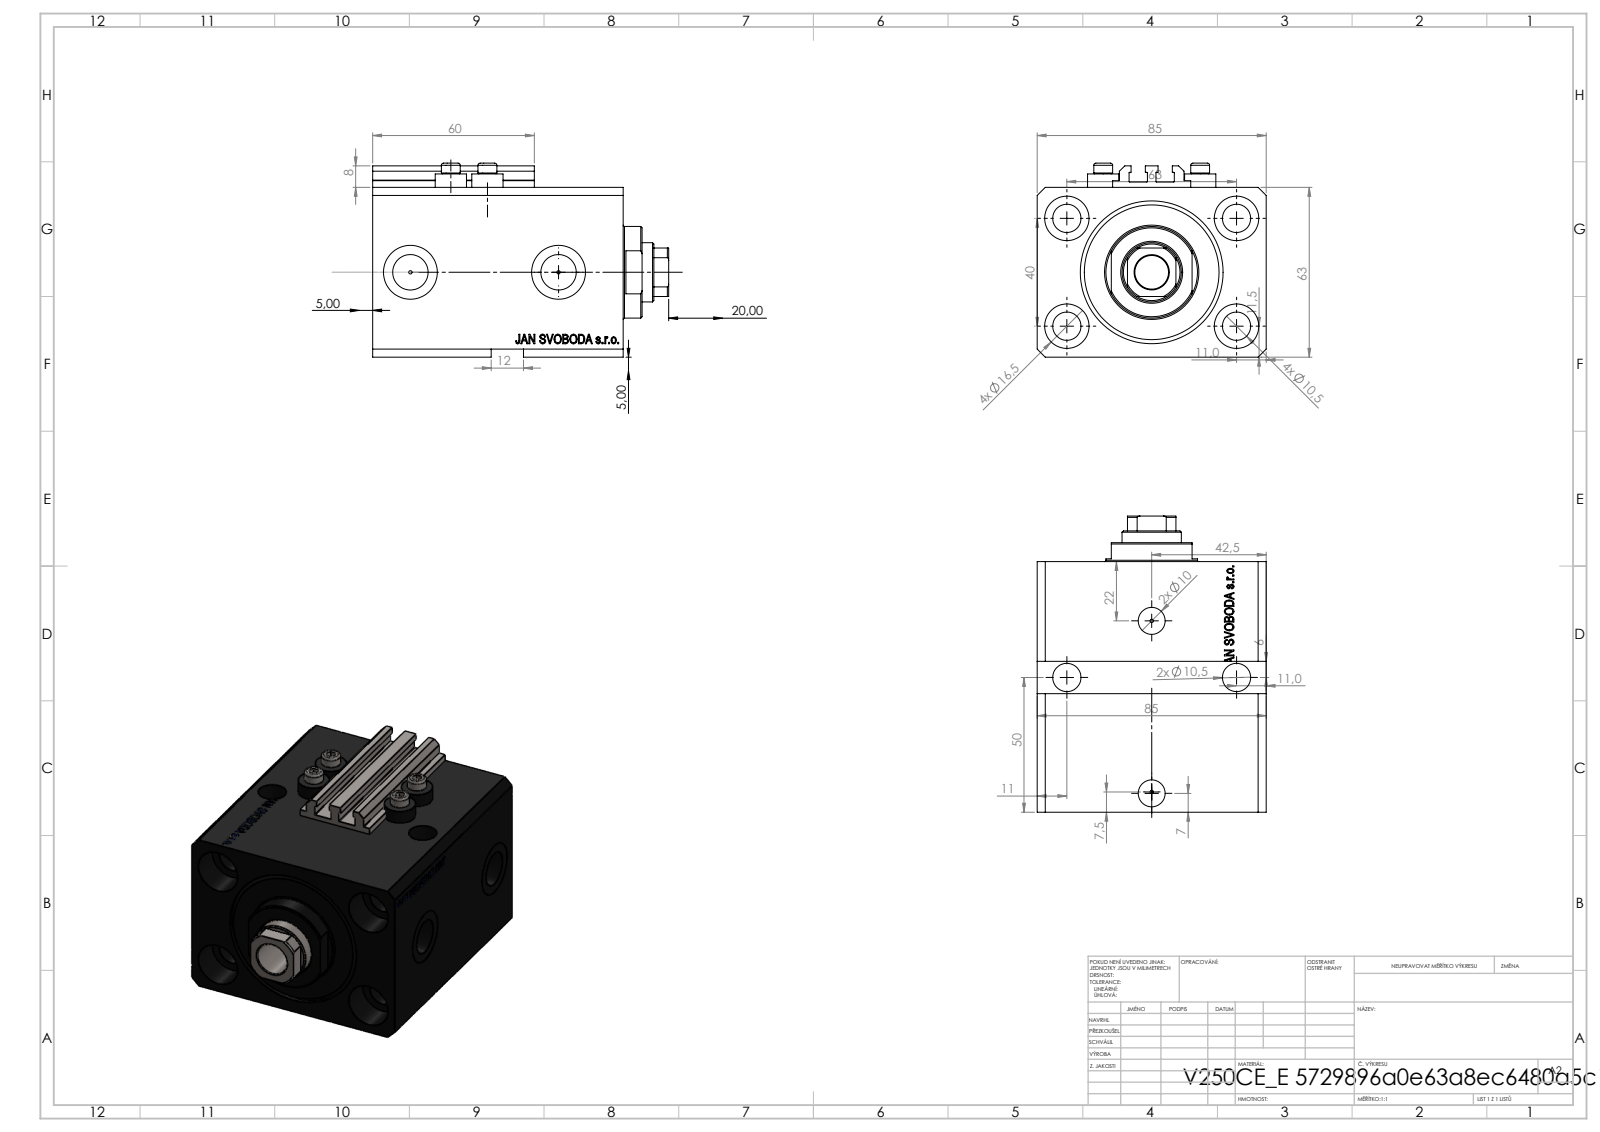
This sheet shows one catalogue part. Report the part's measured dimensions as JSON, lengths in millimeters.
{"part_name": "ALLEN BOLT V250CE; V250CE_C_VCP; V250CE_E_Body; V250CE_VC_E", "step_written_by": "SolidWorks 2019 (CONFIG_CONTROL_DESIGN)", "units": "millimeters", "bodies": {"solids": 8, "faces": 1103, "planar": 539, "cylindrical": 138, "other": 426}, "overall_size": [110, 85, 72], "volume_mm3": 433630, "surface_area_mm2": 96943, "round_holes": [[10.5, 6], [1.25, 4], [4, 4], [16.5, 4], [10, 2], [13.16, 2], [20, 2], [12.5, 1], [22, 1], [40, 1], [53, 1]], "round_bosses_or_shafts": [[11.6, 4], [7, 4], [34, 1]], "partial_cylinders_radius": [[0.2, 10], [10.5, 1]], "face_to_face_distances": [63, 85, 93, 17, 76, 11.4, 64.6, 81.6, 3, 65], "hole_center_spacings": [37.31, 63, 13.6, 15.4, 24.96, 28.02, 28.43, 33.62]}
